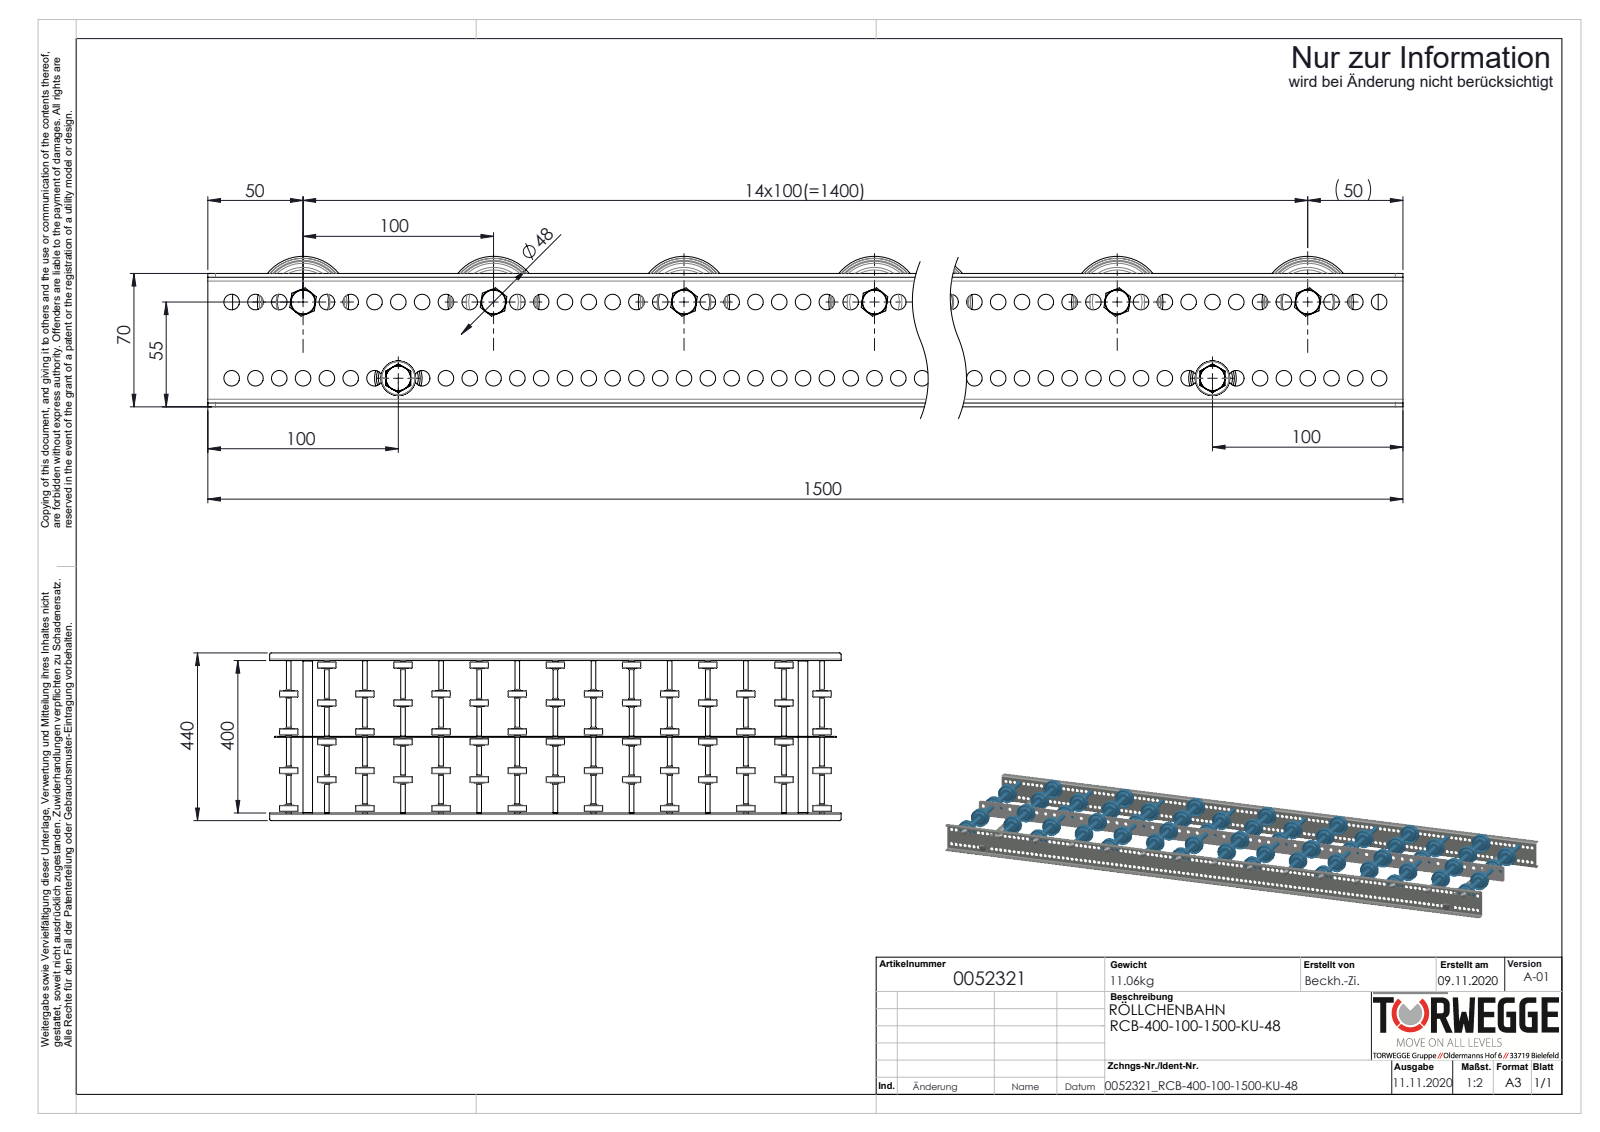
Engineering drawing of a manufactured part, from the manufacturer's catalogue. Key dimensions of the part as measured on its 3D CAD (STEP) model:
Part name (STEP PRODUCT): S100100_Längstraverse-42x2,5_S100102_Lngstraverse-RB-L1500; Traversen_KFG_L400; Röllchenachse-für-Konfiguration_EL400; Profil_LRB-20x70x20x2_KFG_S100201_U-PROFIL-20-70-20-2-LRB-L=1500 (+6 more)
STEP written by: SolidWorks 2020 (AUTOMOTIVE_DESIGN)
Units: millimetres
Bodies: 178 solids, 6820 faces (1176 planar, 2600 cylindrical, 3044 other)
Overall size (bounding box): 1500 × 440 × 79
Volume: 2 531 000 mm³ · Surface area: 1 940 000 mm²
Round holes (diameter × count): ⌀8.2 ×238, ⌀8.5 ×59, ⌀6.65 ×15, ⌀9.65 ×15, ⌀13.7 ×15, ⌀6.8 ×2, ⌀21 ×2
Round bosses / shafts (diameter × count): ⌀8 ×17, ⌀48 ×15, ⌀27 ×15, ⌀12.7 ×15, ⌀12.5 ×15, ⌀12 ×15, ⌀25 ×2
Partial cylindrical surfaces — rounded edges, fillets, slot ends (radius × count): R4 ×8, R2 ×4, R5 ×4
Main face-to-face distances: 2, 402, 68, 404, 400, 201.1, 198.6, 203.4, 200.9, 198.9
Hole centre spacings: 12.5, 25, 37.5, 50, 62.5, 75, 87.5, 100
